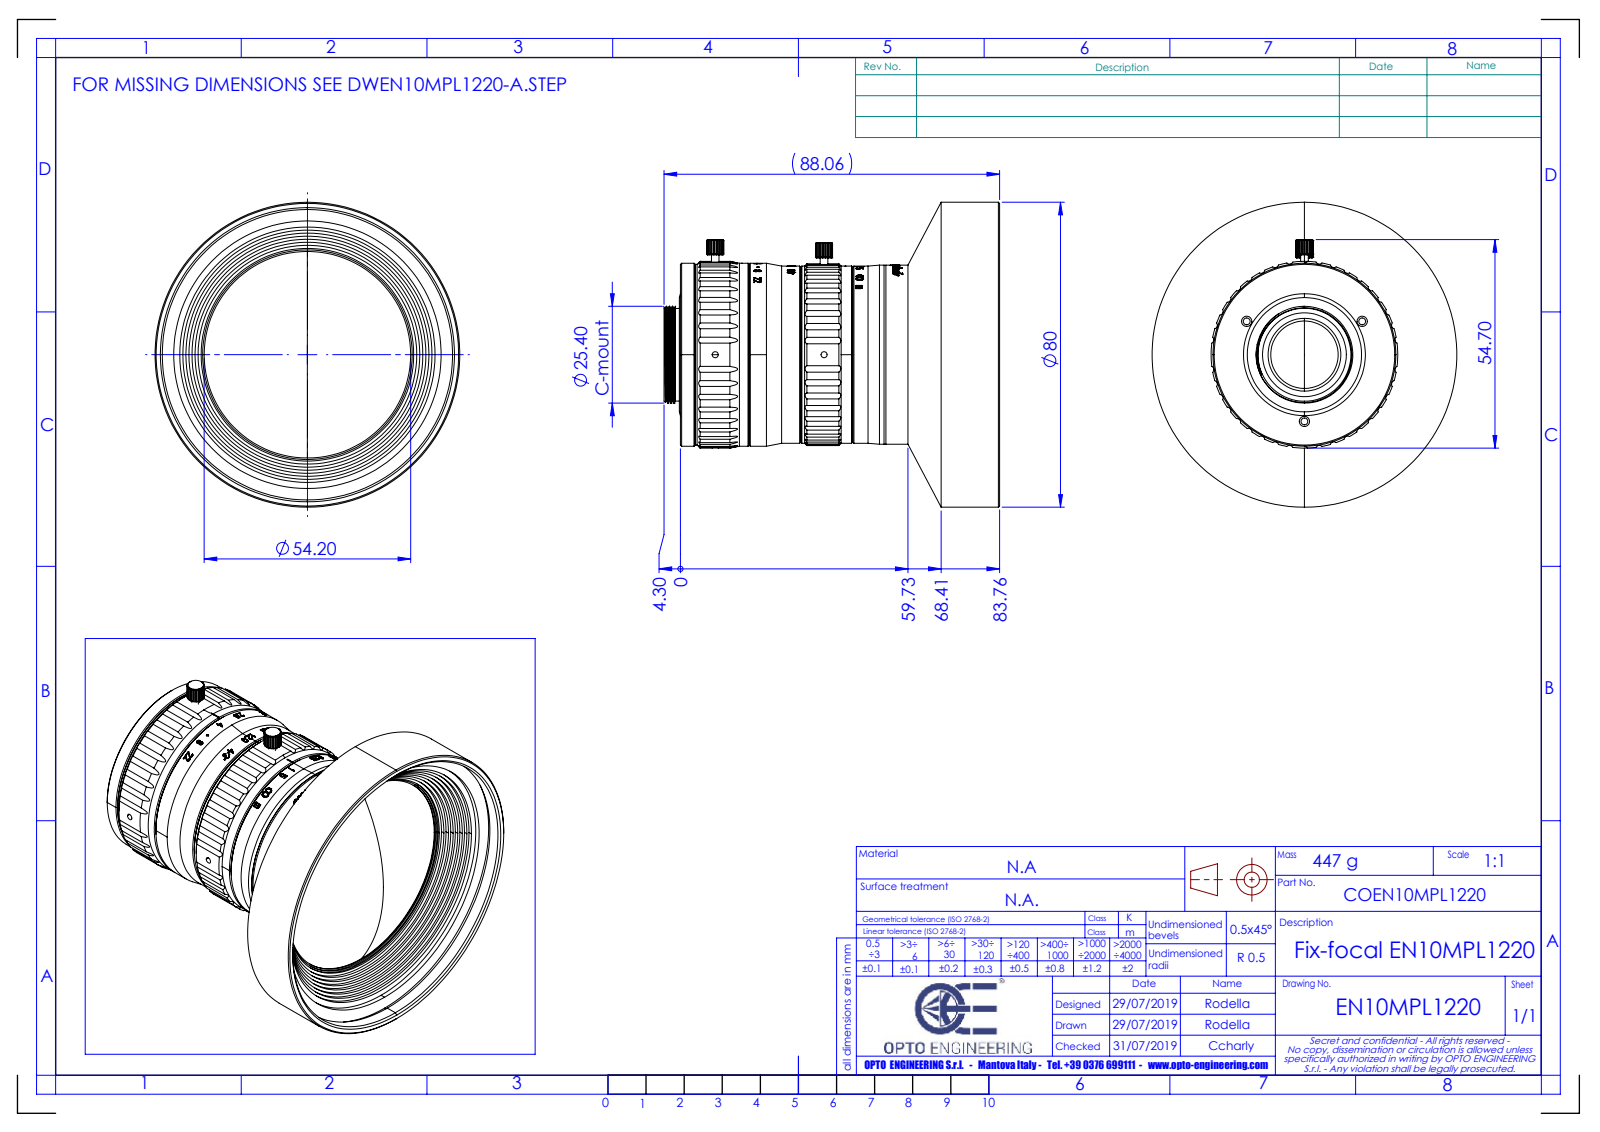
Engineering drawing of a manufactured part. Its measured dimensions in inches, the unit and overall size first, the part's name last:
Units: inches
Overall size (bounding box): 3.467 × 3.15 × 3.15
Round holes (diameter × count): ⌀0.063 ×4, ⌀0.071 ×3, ⌀0.106 ×3, ⌀0.043 ×2, ⌀0.697 ×1, ⌀0.866 ×1, ⌀1.512 ×1, ⌀1.543 ×1, ⌀1.591 ×1, ⌀1.732 ×1, ⌀1.764 ×1, ⌀2.134 ×1
Round bosses / shafts (diameter × count): ⌀0.079 ×2, ⌀3.15 ×1, ⌀1.89 ×1, ⌀1.866 ×1, ⌀1.85 ×1, ⌀1.849 ×1, ⌀1.831 ×1, ⌀1.724 ×1
Partial cylindrical surfaces — rounded edges, fillets, slot ends (radius × count): R0.039 ×72, R0.059 ×4, R0.089 ×2, R0.898 ×1, R0.913 ×1, R0.914 ×1, R0.923 ×1, R0.939 ×1
Main face-to-face distances: 1.07, 0.538, 0.532, 1.781, 1.243, 0.711, 1.34, 1.878, 2.41, 3.12
Hole centre spacings: 0.689, 0.68, 0.835, 0.863, 1.124, 1.193, 1.52, 0.236
Volume: 8.333 in³ · Surface area: 66.55 in²
Bodies: 8 solids, 1923 faces (489 planar, 369 cylindrical, 1065 other)
Part name (STEP PRODUCT): FAL0011-0E-101-WX; FAL0011-0E-104; FAL0011-0E-105-WX; FAL0011-0E-106 (+4 more)
STEP written by: PRO/ENGINEER BY PARAMETRIC TECHNOLOGY CORPORATION, 2013230 (CONFIG_CONTROL_DESIGN)
